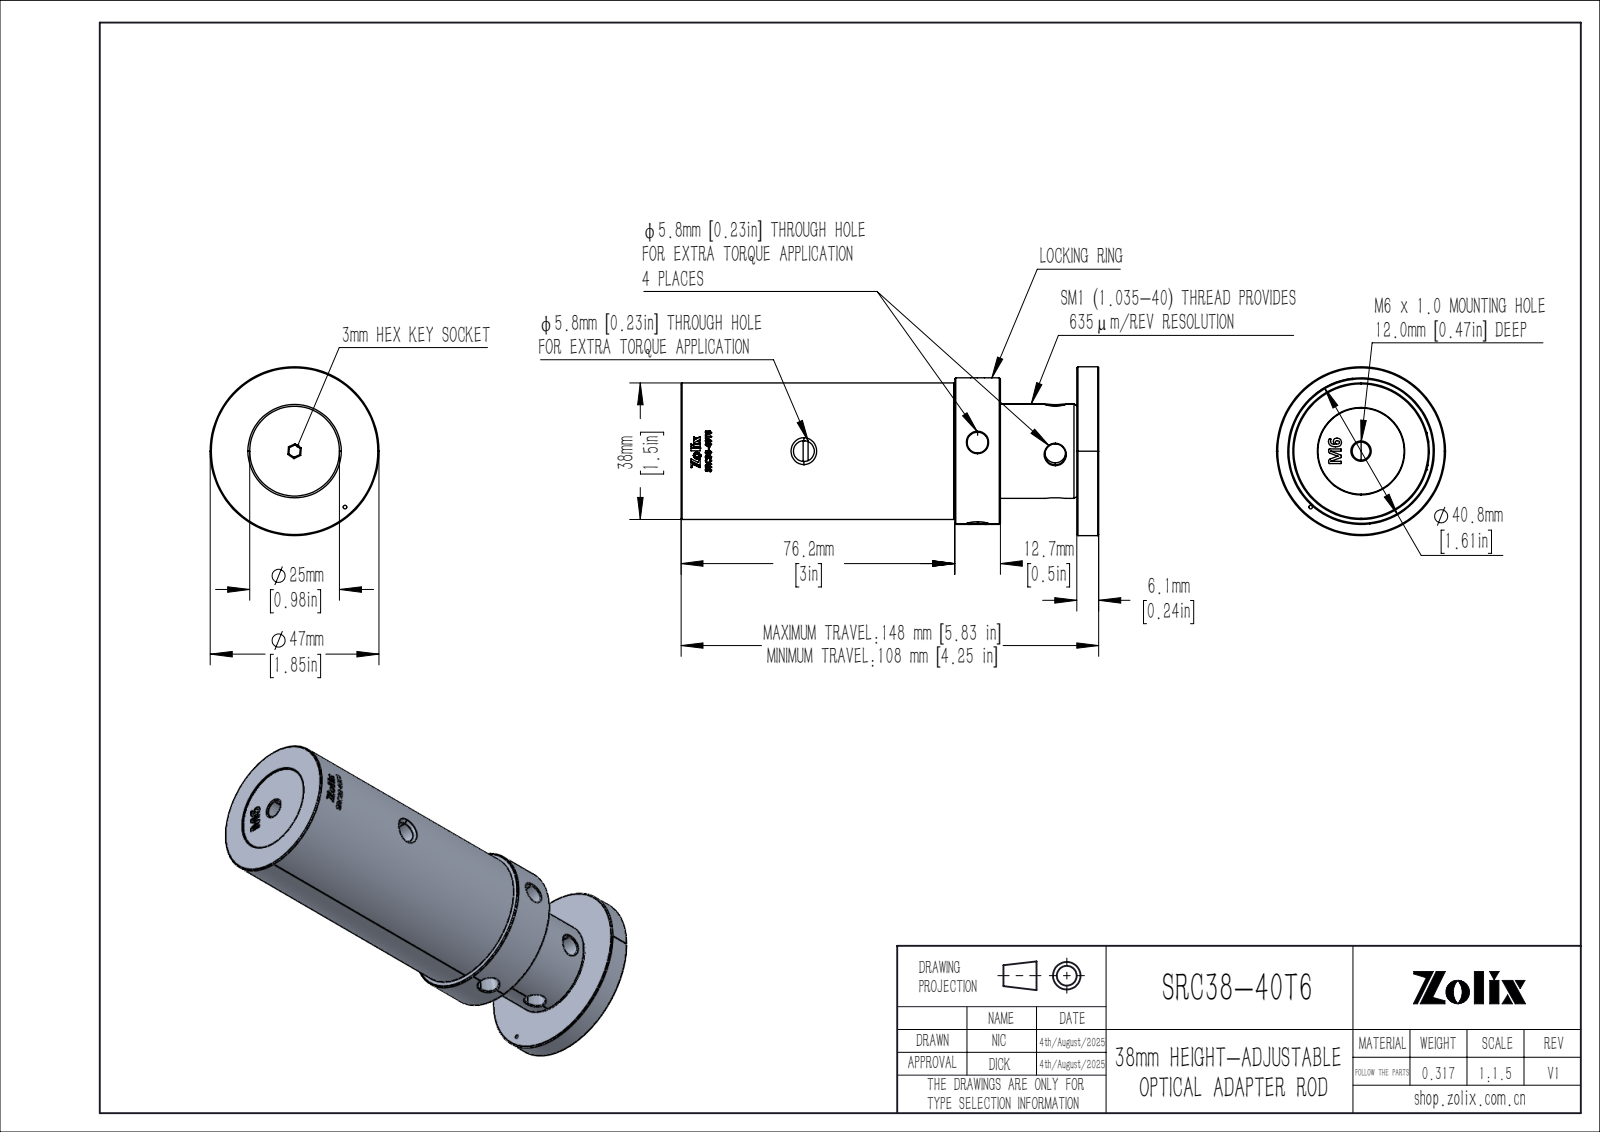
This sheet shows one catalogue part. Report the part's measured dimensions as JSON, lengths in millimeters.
{"part_name": "SRC38-40T6", "step_written_by": "SolidWorks 2020 (CONFIG_CONTROL_DESIGN)", "units": "millimeters", "bodies": {"solids": 4, "faces": 495, "planar": 87, "cylindrical": 72, "other": 336}, "overall_size": [116.3, 47, 47], "volume_mm3": 117475, "surface_area_mm2": 33218, "round_holes": [[5.8, 7], [1, 1], [5, 1], [21, 1], [25.6, 1], [27.3, 1]], "round_bosses_or_shafts": [[47, 1], [40.8, 1], [38, 1], [26.3, 1], [6, 1], [4.4, 1]], "partial_cylinders_radius": [[18.98, 1]], "face_to_face_distances": [34, 6.1, 40.1, 76.2, 27.4, 21.3, 12.7, 88.9, 116.3, 110.2], "hole_center_spacings": [20.97]}
